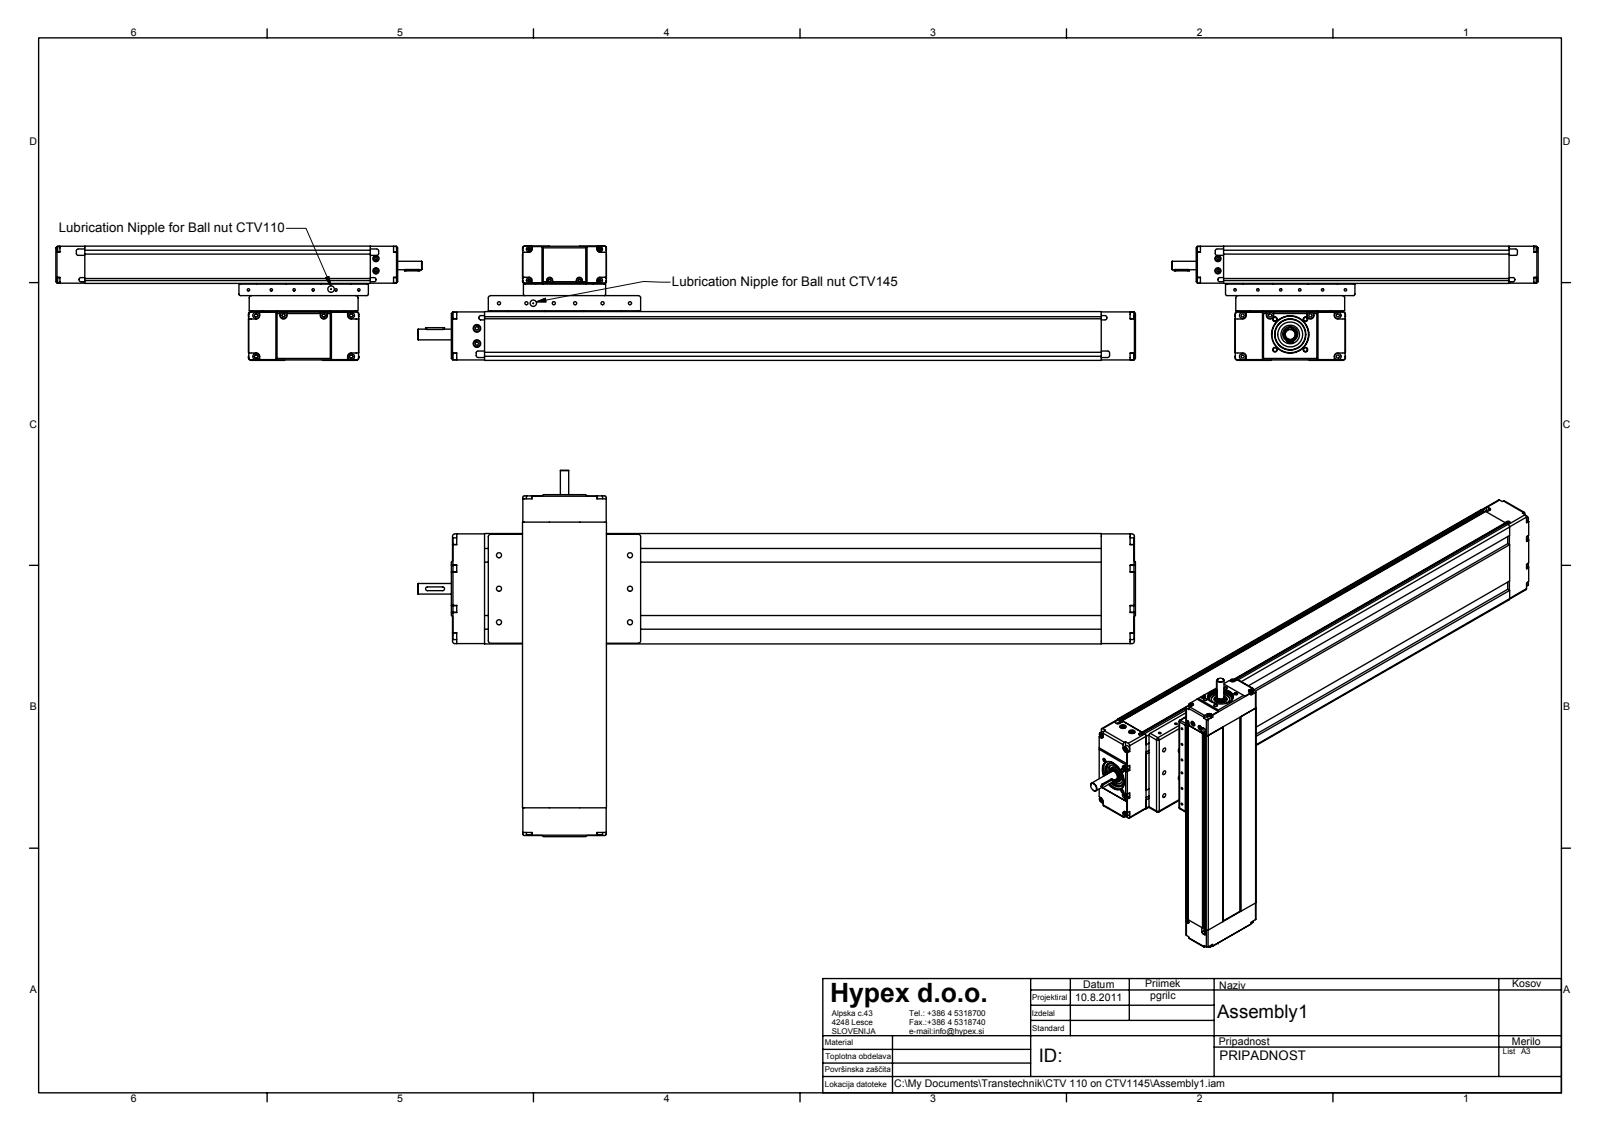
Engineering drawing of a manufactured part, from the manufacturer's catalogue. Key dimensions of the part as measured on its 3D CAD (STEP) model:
Part name (STEP PRODUCT): CTV 145 L IPART-021; CTV 110 L IPART-02
STEP written by: Autodesk Inventor 2012 (AUTOMOTIVE_DESIGN)
Units: millimetres
Bodies: 2 solids, 1165 faces (720 planar, 288 cylindrical, 157 other)
Overall size (bounding box): 942.5 × 481 × 150
Volume: 11 210 000 mm³ · Surface area: 764 174 mm²
Round holes (diameter × count): ⌀4.92 ×25, ⌀4.13 ×14, ⌀6.65 ×9, ⌀3.24 ×6, ⌀7 ×6, ⌀8.5 ×6, ⌀9 ×6, ⌀1.7 ×4, ⌀5 ×4, ⌀6 ×4, ⌀4.2 ×2, ⌀8 ×2
Round bosses / shafts (diameter × count): ⌀8.5 ×8, ⌀7 ×8, ⌀1 ×6, ⌀4 ×2, ⌀24.36 ×1, ⌀20 ×1, ⌀19.77 ×1, ⌀17 ×1
Partial cylindrical surfaces — rounded edges, fillets, slot ends (radius × count): R2 ×18, R2.5 ×18, R3 ×16, R0.91 ×8, R4 ×6, R4.75 ×6, R2.25 ×4, R2.55 ×4
Main face-to-face distances: 1, 64, 85, 0.5, 84, 100, 65, 63, 21, 36
Hole centre spacings: 18, 36, 89.82, 100, 88, 25.1, 50, 52.97
